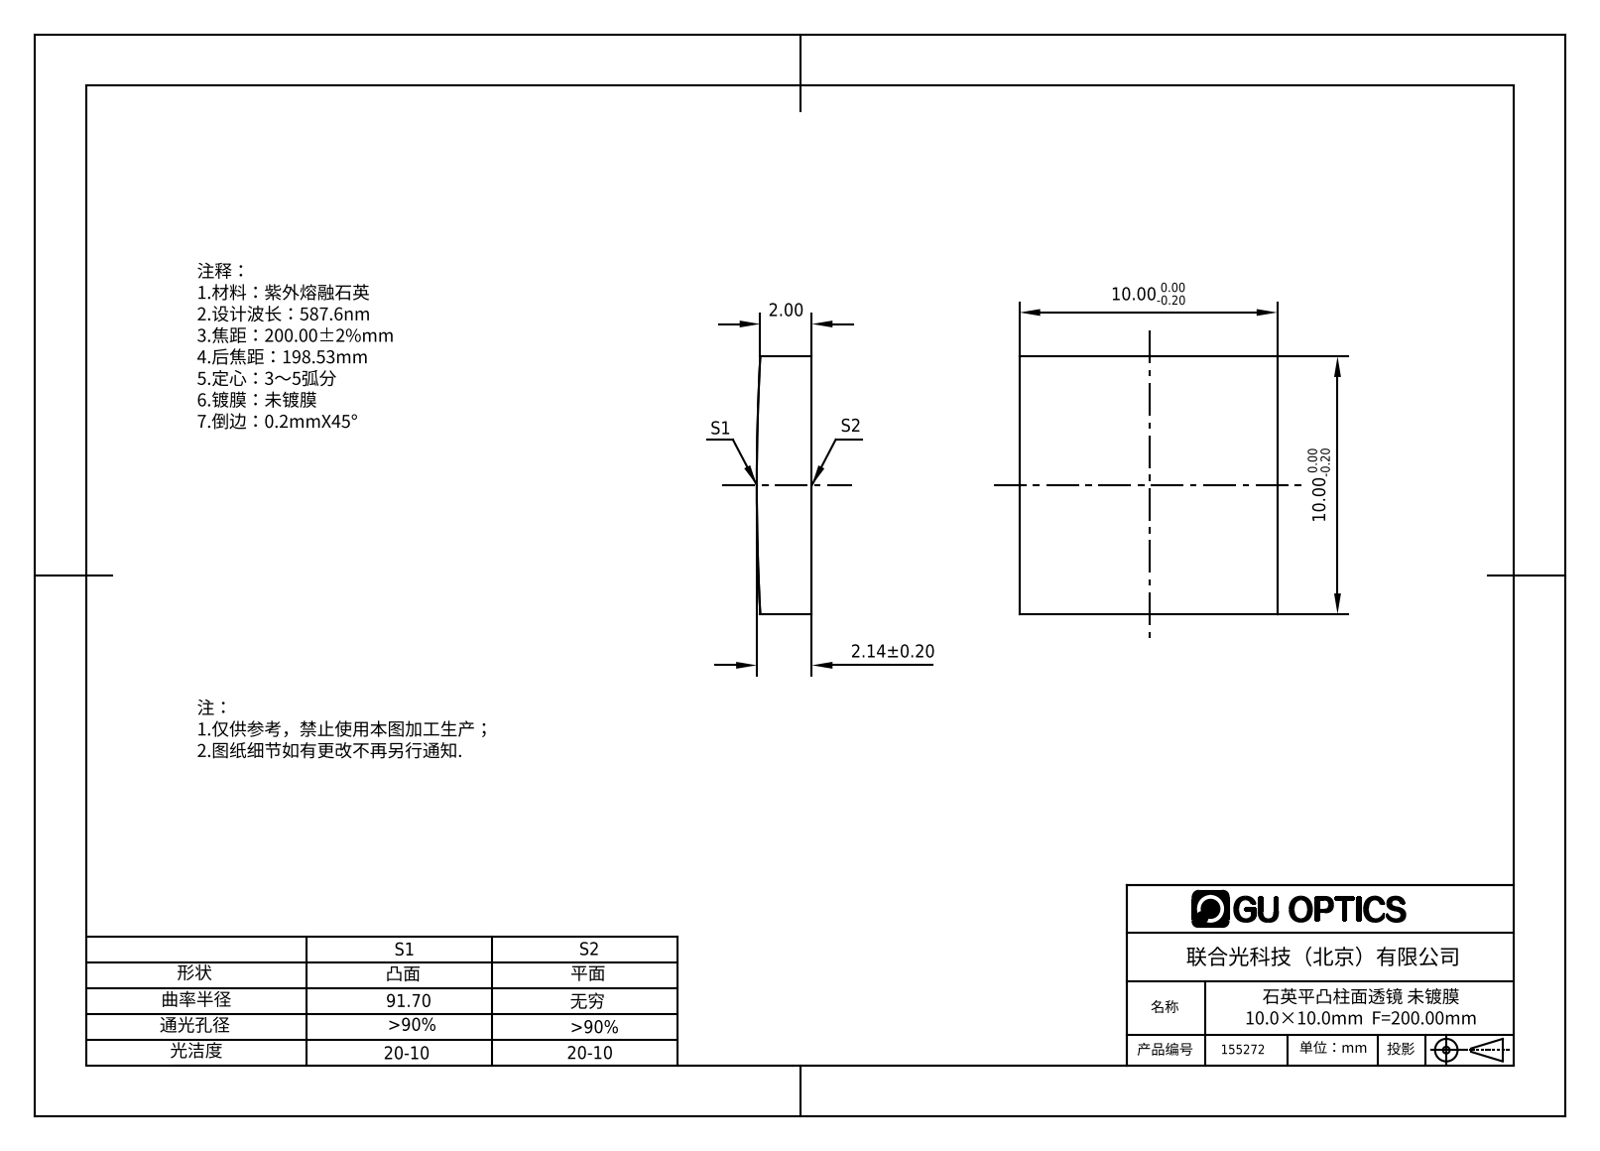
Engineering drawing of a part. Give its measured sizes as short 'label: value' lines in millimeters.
name: 155272
written by: SolidWorks 2016 (AUTOMOTIVE_DESIGN)
unit: mm
bodies: 1 solid, 6 faces (5 planar, 1 cylindrical, 0 other)
size: 10 × 10 × 2.14
volume: 209 mm³; area: 282 mm²
rounds: 1× R91.7
face distances: 10
